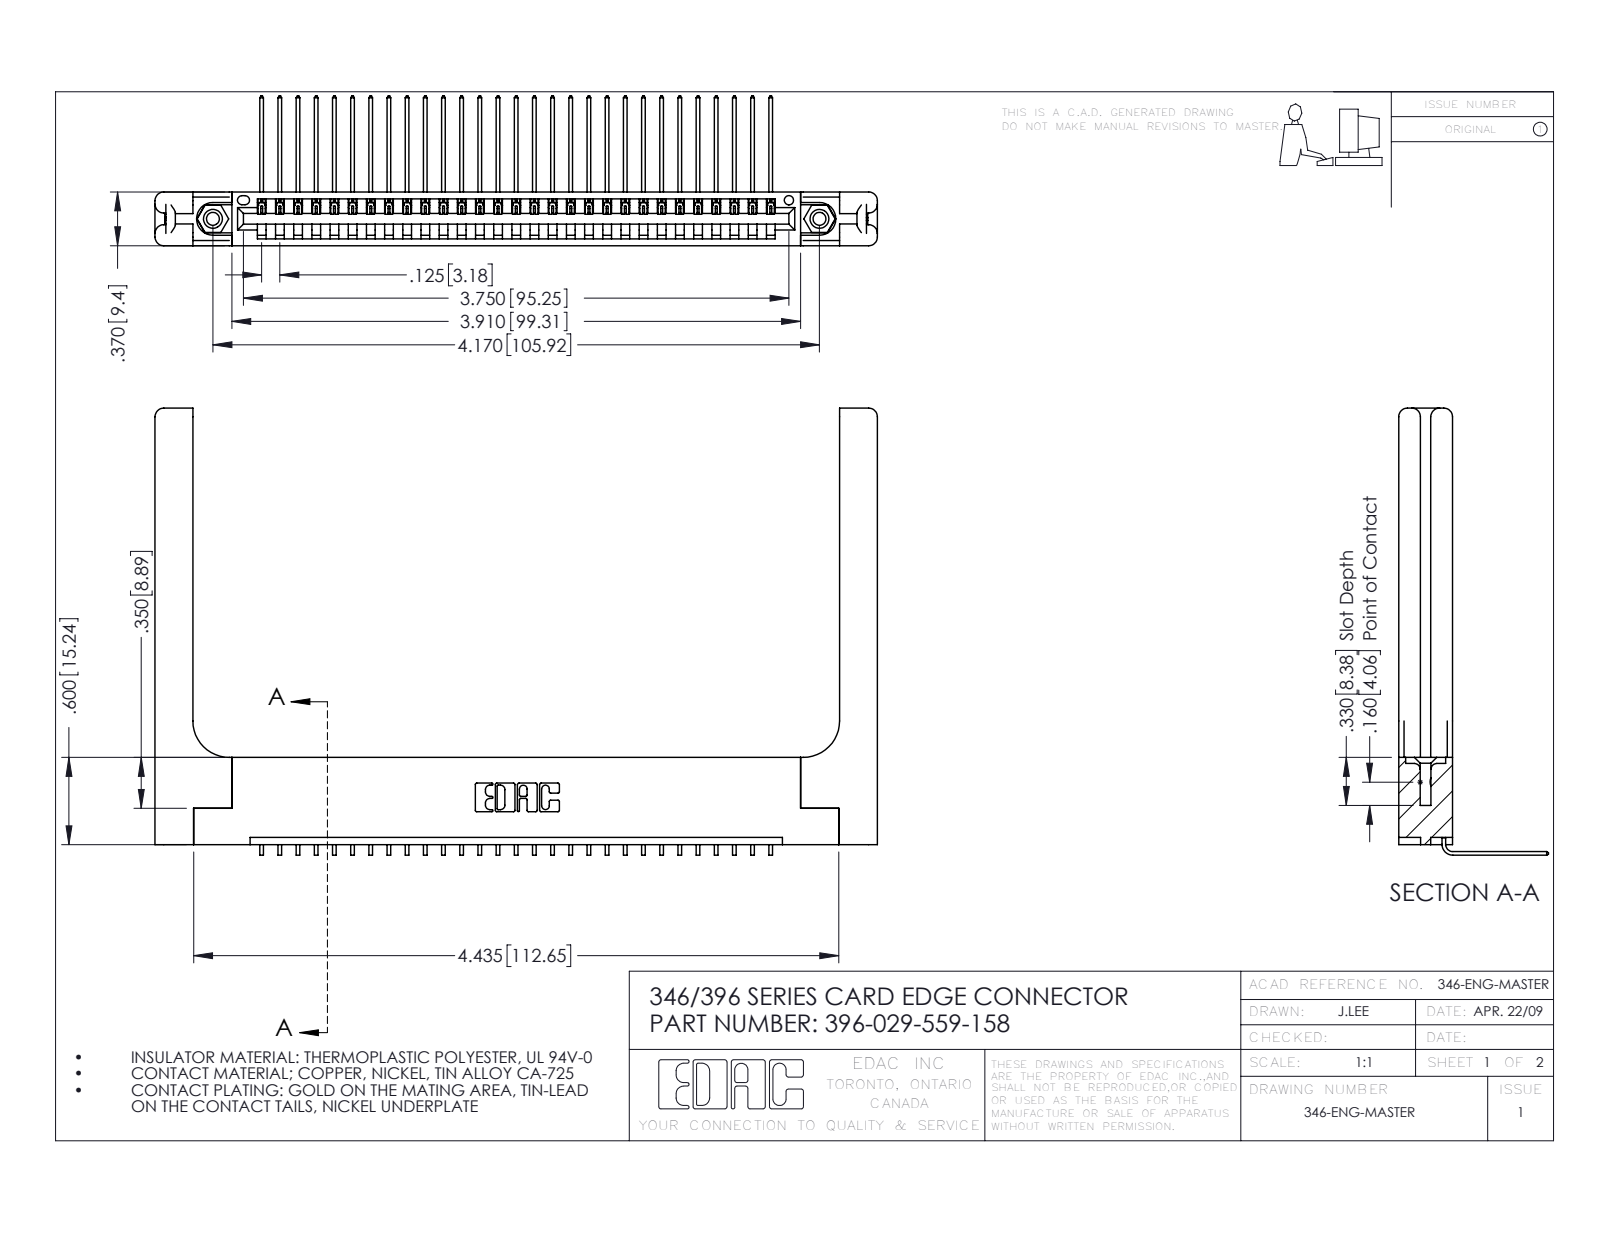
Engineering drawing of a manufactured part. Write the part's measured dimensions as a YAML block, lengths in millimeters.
part_name: "346 Part_Flush Mounting Lugs - 0.156 Dia-TH; 345-292-001_558 559 Tail - 1; 396-029-559-158; 345-250-001_345-250-001-102 (+1 more)"
step_written_by: "SolidWorks 2016 (CONFIG_CONTROL_DESIGN)"
units: millimeters
bodies: {solids: 34, faces: 2118, planar: 1442, cylindrical: 616, other: 60}
overall_size: [126.1, 78.1, 26.2]
volume: 19600
surface_area: 20700
round_holes:
  - {diameter: 2.3, count: 2}
  - {diameter: 3.2, count: 2}
  - {diameter: 4, count: 2}
  - {diameter: 1.6, count: 1}
round_bosses_or_shafts:
  - {diameter: 3.9, count: 2}
partial_cylinders:
  - {radius: 0.2, count: 58}
  - {radius: 0.3, count: 22}
  - {radius: 1.5, count: 16}
  - {radius: 0.2, count: 6}
  - {radius: 0.8, count: 6}
  - {radius: 0.7, count: 3}
  - {radius: 0.8, count: 2}
  - {radius: 0.8, count: 2}
face_to_face_distances: [9.4, 1.8, 1.2, 8.2, 3.8, 3.8, 0.6, 6.4, 7.6, 1.9]
hole_center_spacings: [6.2, 100.6, 105.9]
